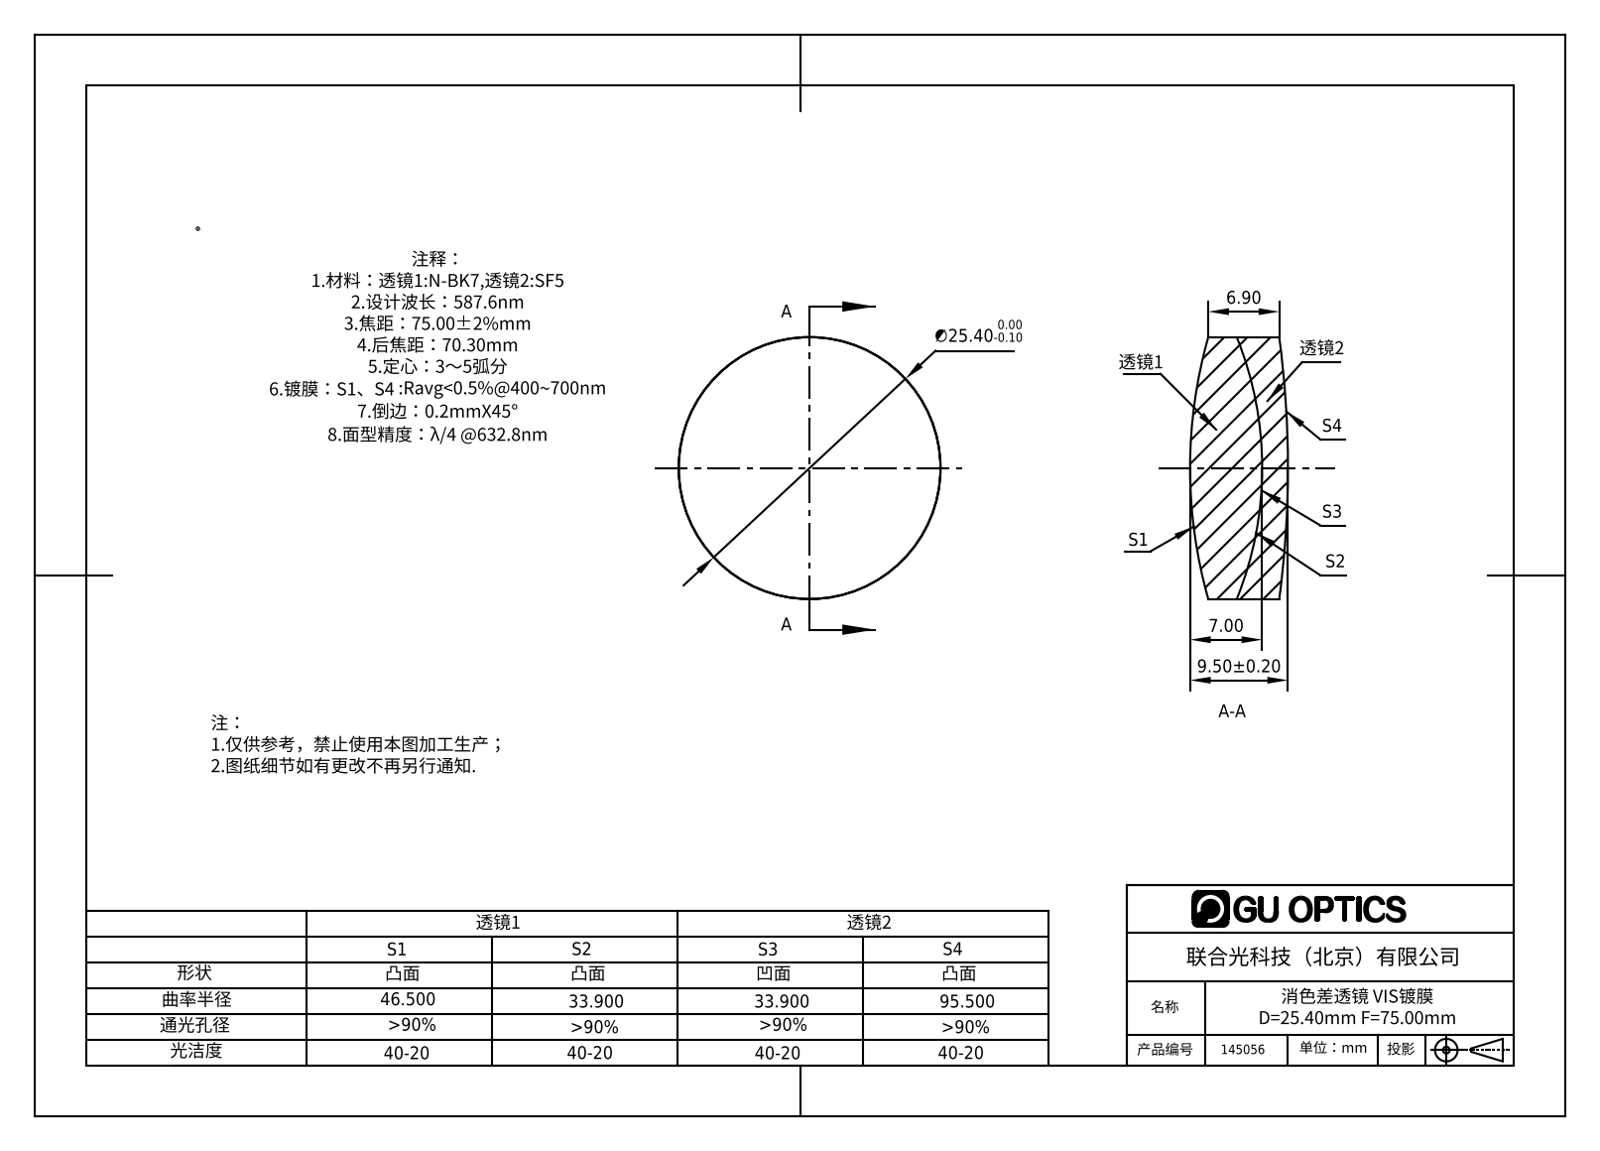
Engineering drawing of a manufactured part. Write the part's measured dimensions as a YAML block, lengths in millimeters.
part_name: "145056"
step_written_by: "SolidWorks 2016 (AUTOMOTIVE_DESIGN)"
units: millimeters
bodies: {solids: 2, faces: 12, planar: 0, cylindrical: 4, other: 8}
overall_size: [25.4, 25.4, 9.5]
volume: 4154
surface_area: 2627
round_bosses_or_shafts:
  - {diameter: 25.4, count: 1}
